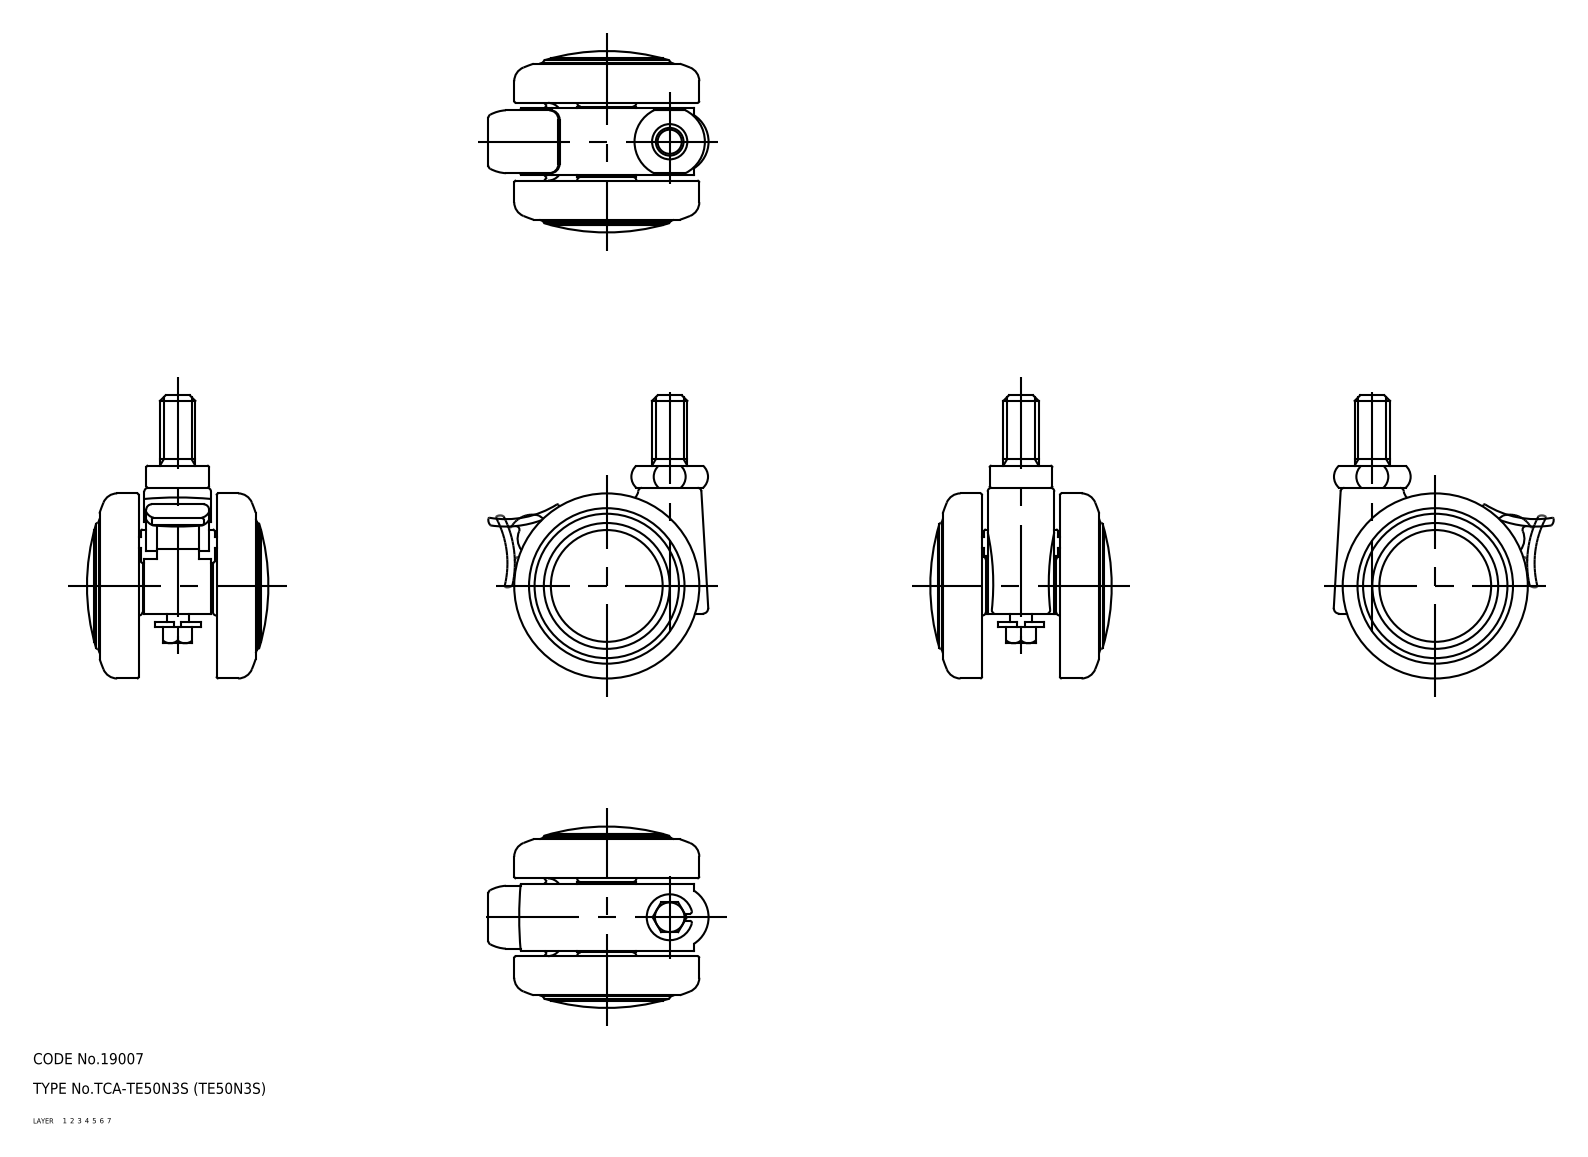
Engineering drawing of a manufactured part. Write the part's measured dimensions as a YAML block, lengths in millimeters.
part_name: "wheel; main shaft; lever; TE50N3S_3445_36"
step_written_by: "CADfix (AUTOMOTIVE_DESIGN)"
units: millimeters
bodies: {solids: 5, faces: 231, planar: 0, cylindrical: 0, other: 231}
overall_size: [76.5, 59.42, 49]
volume: 63527
surface_area: 27662
